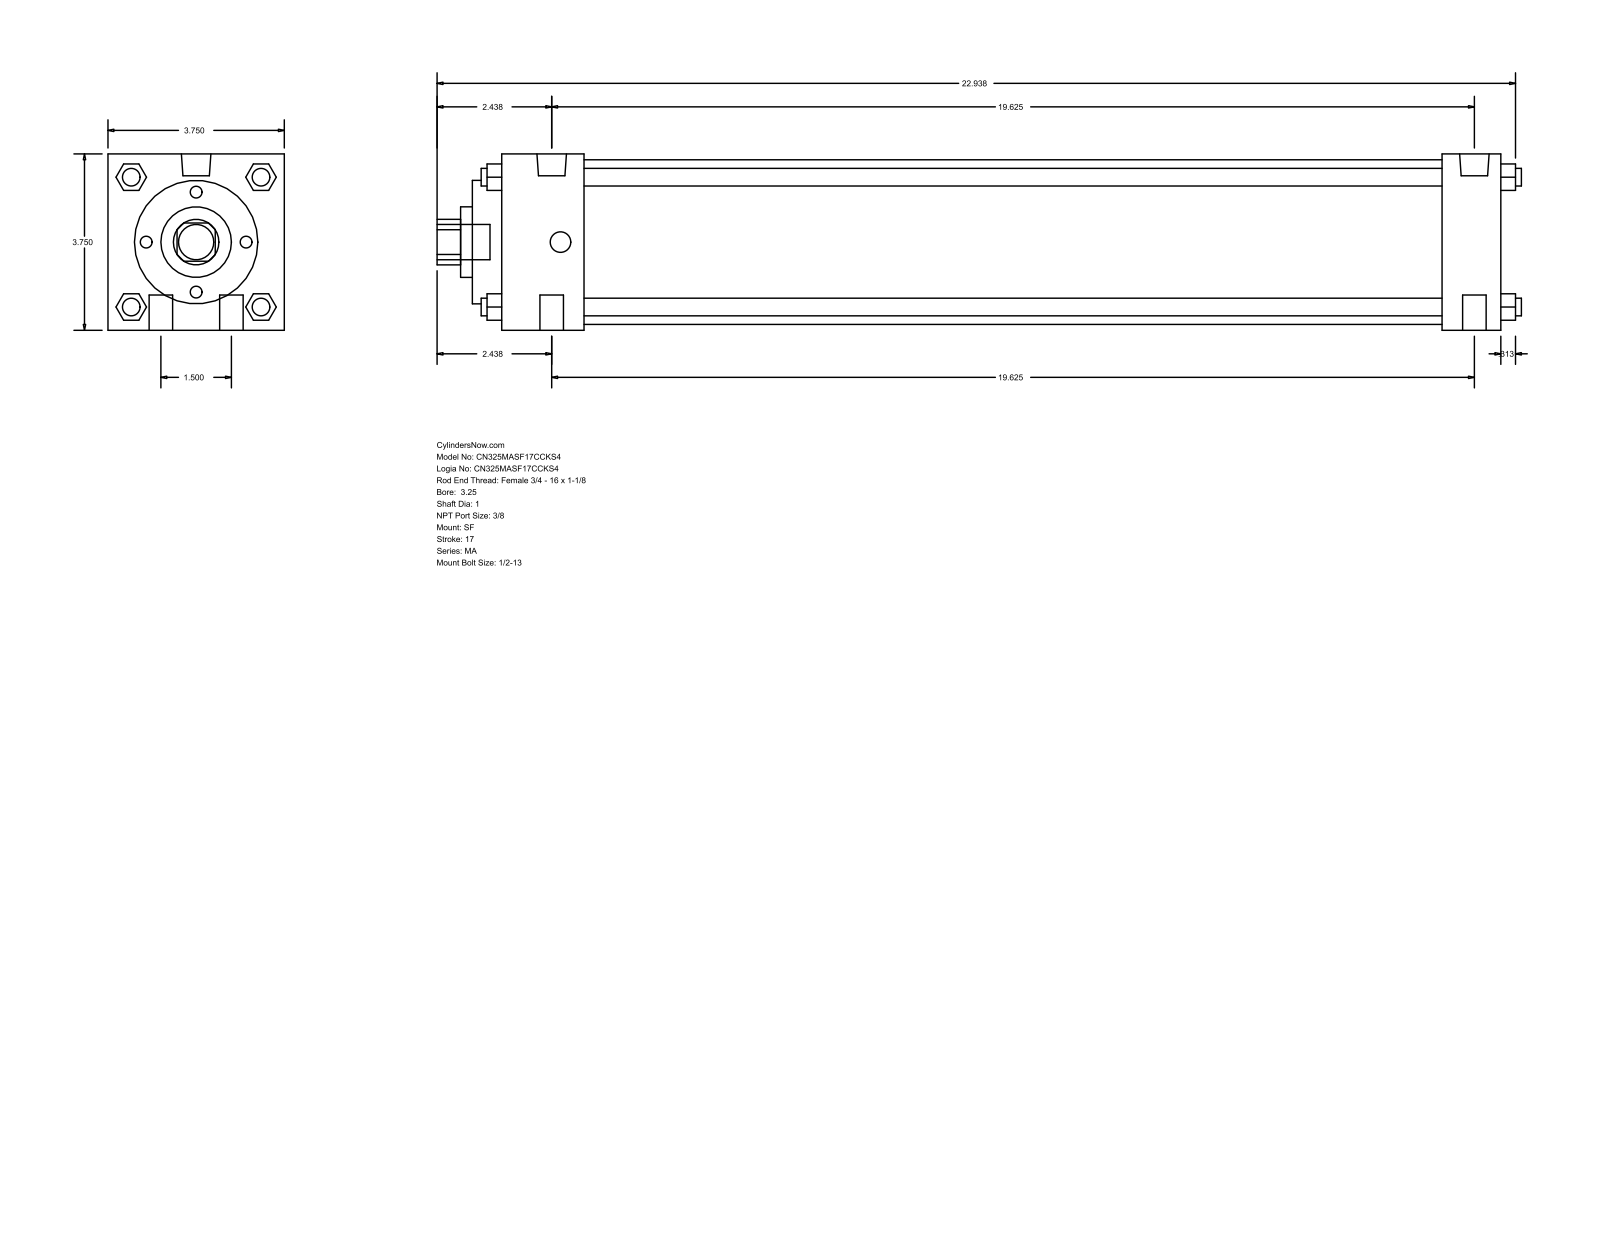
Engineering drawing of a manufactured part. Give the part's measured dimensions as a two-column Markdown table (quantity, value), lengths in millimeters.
| quantity | value |
| --- | --- |
| part name | MA_SF__0325_1 |
| STEP written by | GSSL Pune (CONFIG_CONTROL_DESIGN) |
| units | millimeters |
| bodies | 0 solids, 126 faces (95 planar, 31 cylindrical, 0 other) |
| overall size | 585.79 × 95.25 × 95.25 |
| round holes (diameter × count) | 25.4 × 1, 38.1 × 1, 66.67 × 1, 88.9 × 1 |
| round bosses / shafts (diameter × count) | 12.7 × 4, 9.53 × 4, 15.93 × 2, 11.11 × 2, 19.05 × 1 |
| partial cylindrical surfaces (radius × count) | 12.29 × 1 |
| main face-to-face distances | 95.24, 539.75, 555.62, 15.87, 508, 31.75, 44.46, 463.54, 495.29, 60.33 |
